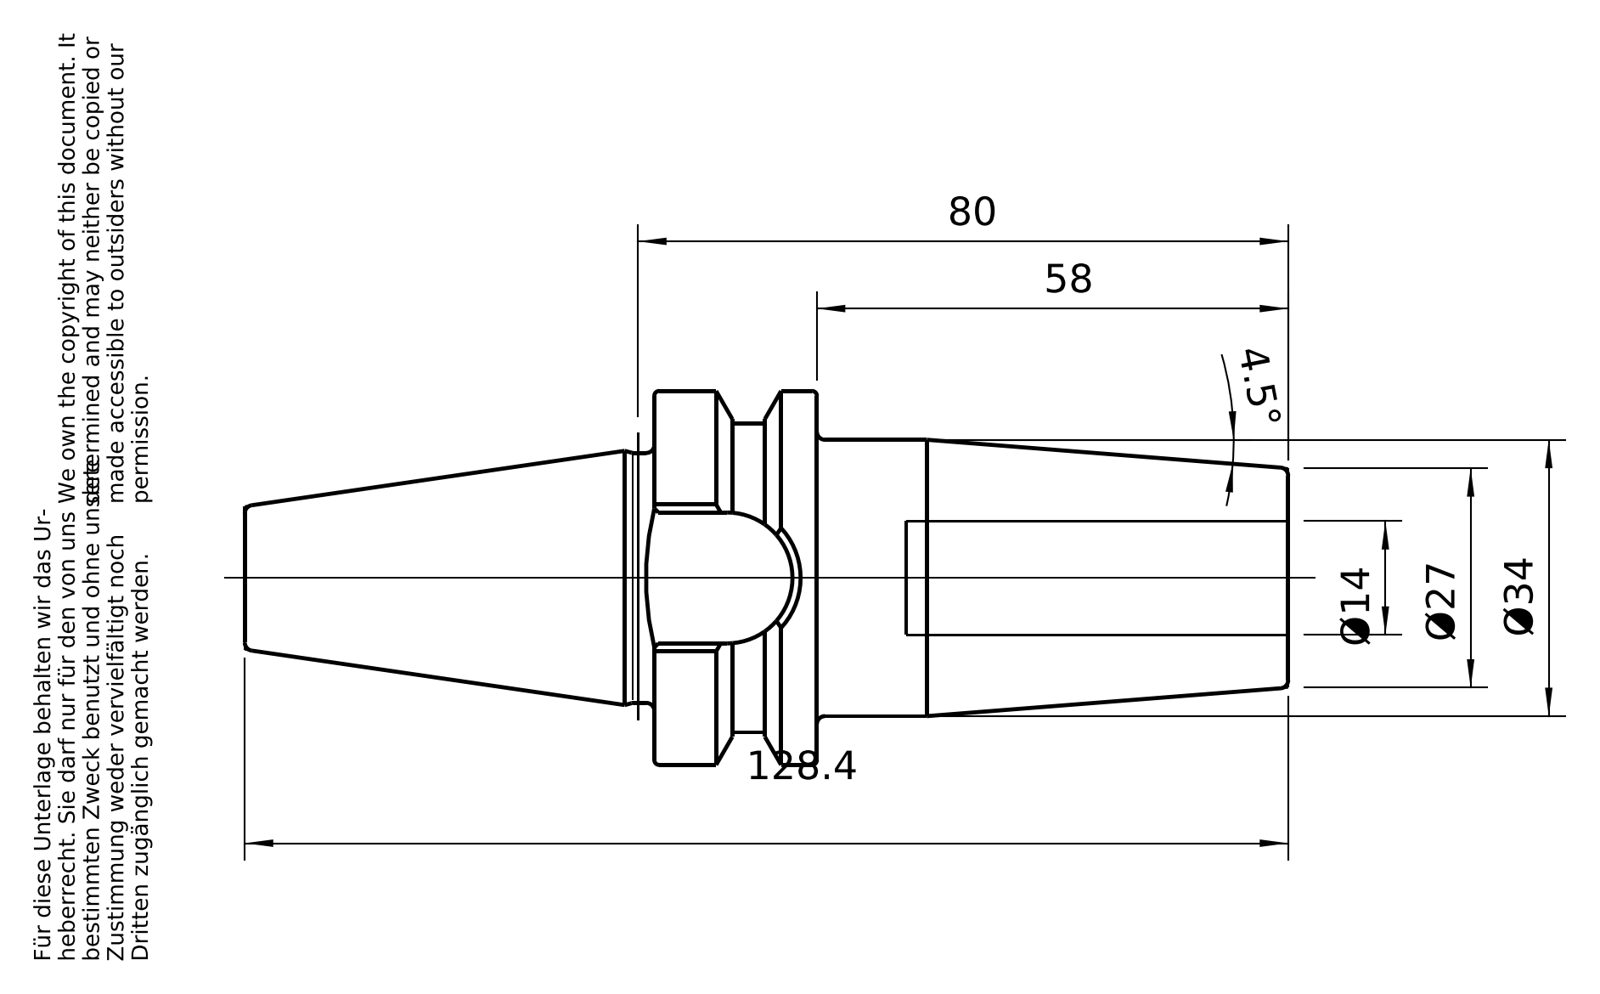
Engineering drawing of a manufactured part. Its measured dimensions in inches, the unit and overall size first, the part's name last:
Units: inches
Overall size (bounding box): 5.055 × 1.81 × 1.81
Round holes (diameter × count): ⌀0.398 ×1, ⌀0.493 ×1, ⌀0.512 ×1, ⌀0.551 ×1
Round bosses / shafts (diameter × count): ⌀1.81 ×1, ⌀1.339 ×1, ⌀1.211 ×1, ⌀0.473 ×1
Partial cylindrical surfaces — rounded edges, fillets, slot ends (radius × count): R0.319 ×1, R0.743 ×1
Main face-to-face distances: 0.787, 3.071, 2.283, 1.272, 1.22, 0.433, 1.85, 0.638, 1.984, 2.772
Volume: 5.322 in³ · Surface area: 29.79 in²
Bodies: 1 solid, 96 faces (26 planar, 22 cylindrical, 48 other)
Part name (STEP PRODUCT): 30-640-14
STEP written by: PRO/ENGINEER BY PARAMETRIC TECHNOLOGY CORPORATION, 2010430 (CONFIG_CONTROL_DESIGN)
